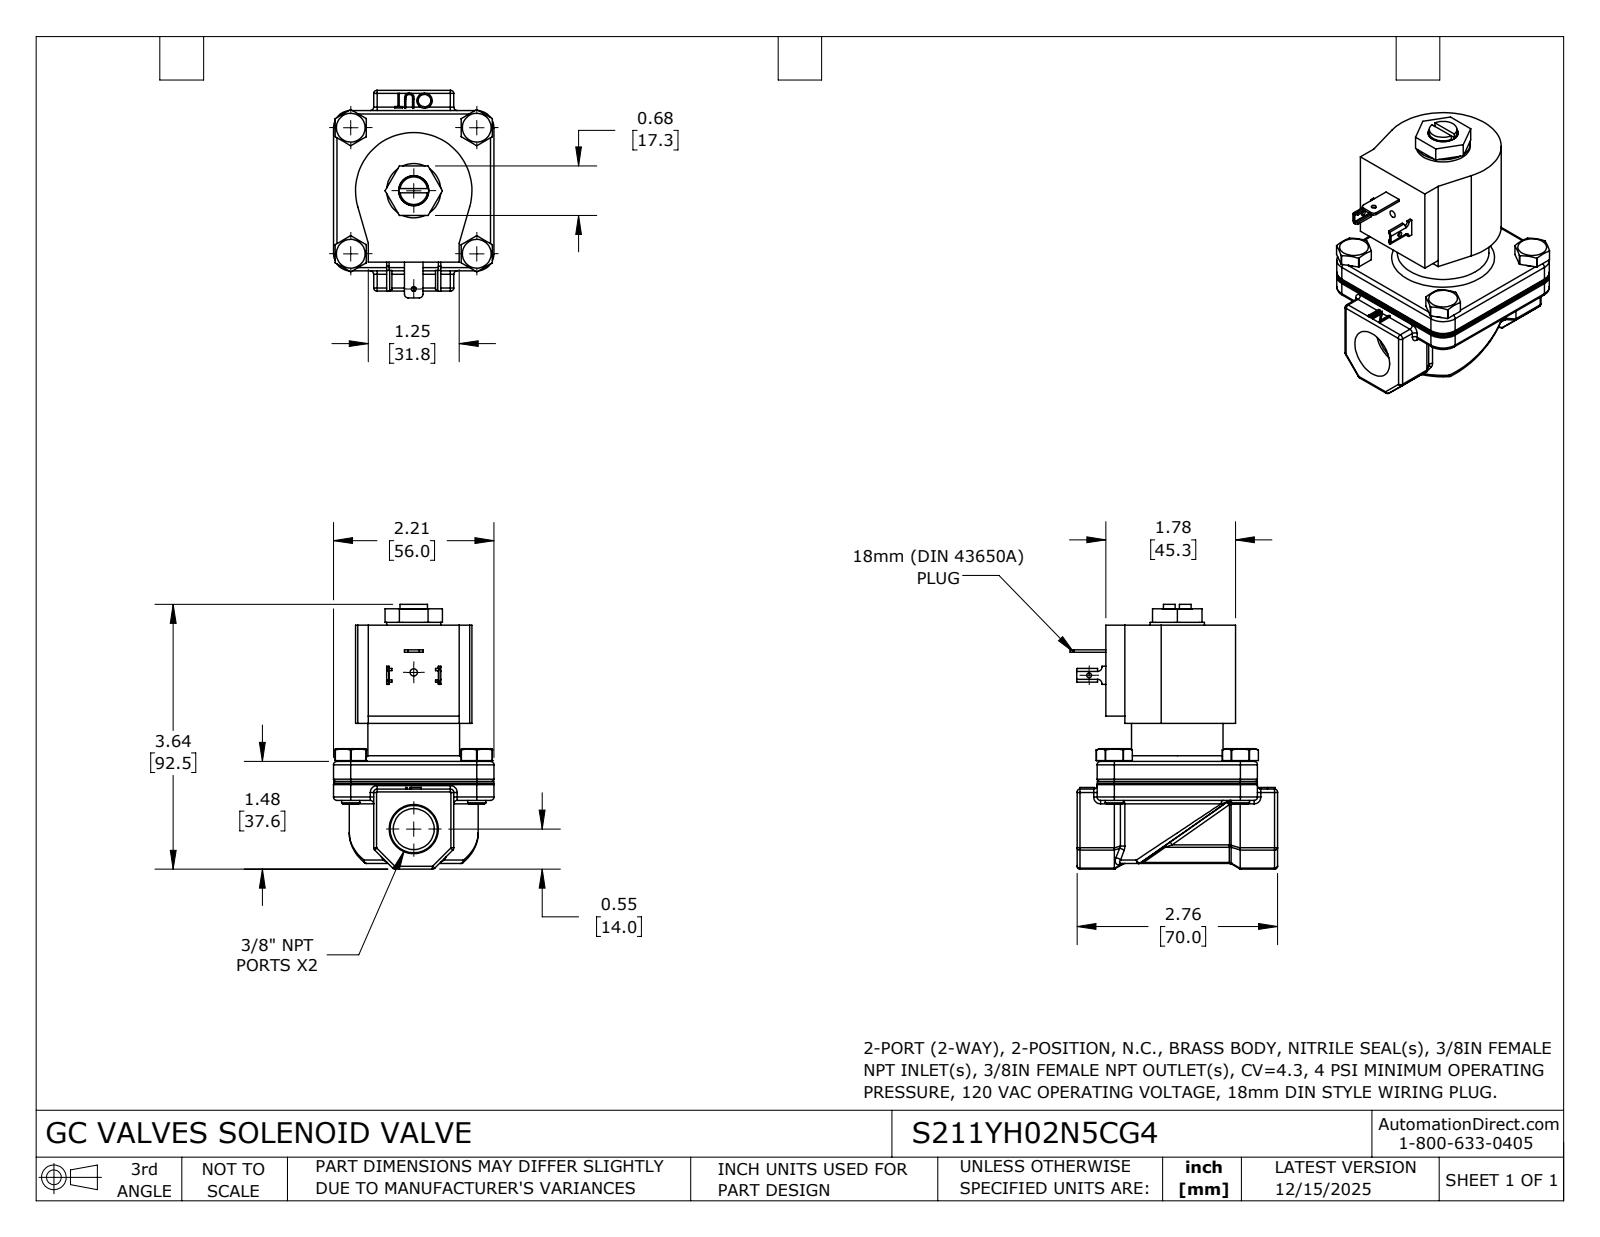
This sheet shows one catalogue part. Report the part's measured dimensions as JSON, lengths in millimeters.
{"part_name": "S211YH02N5CG4", "step_written_by": "SolidWorks 2024 (CONFIG_CONTROL_DESIGN)", "units": "millimeters", "bodies": {"solids": 1, "faces": 507, "planar": 228, "cylindrical": 151, "other": 128}, "overall_size": [92.5, 72.4, 56], "volume_mm3": 150200, "surface_area_mm2": 25060, "round_holes": [[1.7, 1], [1.7, 1], [2.5, 1], [14.3, 1]], "round_bosses_or_shafts": [[10.3, 4], [6.4, 4], [32, 1], [18.9, 1], [9.7, 1]], "partial_cylinders_radius": [[1.2, 57], [1, 12], [0.2, 4], [0.8, 4], [1, 4], [5.9, 4], [6, 4], [1.3, 2]], "face_to_face_distances": [47.6, 14, 42, 56, 13.6, 61.2, 7, 63, 26.9, 13.3], "hole_center_spacings": [54.7]}
